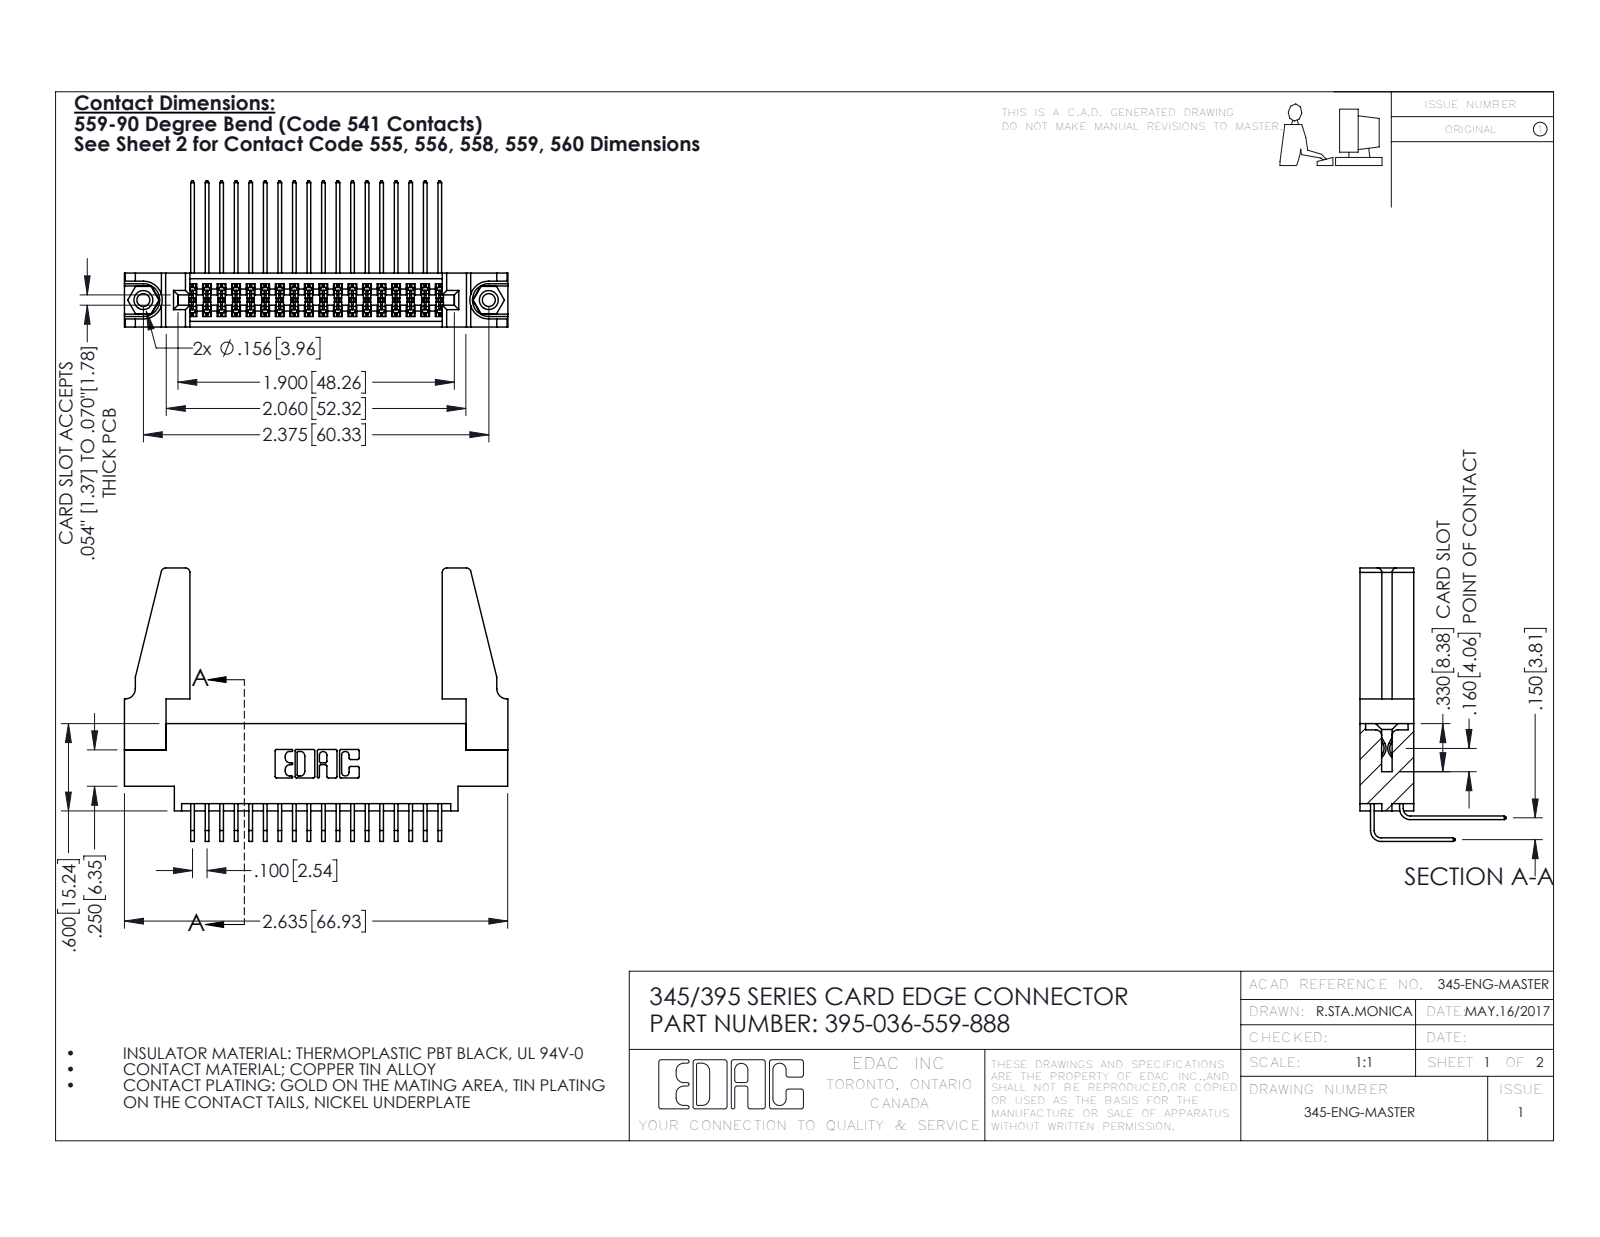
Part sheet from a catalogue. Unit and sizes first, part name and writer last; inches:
Units: inches
Overall size (bounding box): 2.636 × 1.879 × 1.005
Round holes (diameter × count): ⌀0.089 ×2, ⌀0.125 ×2, ⌀0.156 ×2, ⌀0.064 ×1
Round bosses / shafts (diameter × count): ⌀0.155 ×2
Partial cylindrical surfaces — rounded edges, fillets, slot ends (radius × count): R0.006 ×54, R0.01 ×22, R0.03 ×8, R0.007 ×6, R0.031 ×6, R0.026 ×3, R0.014 ×2, R0.019 ×2
Main face-to-face distances: 0.37, 0.072, 0.298, 0.2, 0.098, 0.272, 0.025, 0.15, 0.225, 0.175
Hole centre spacings: 0.27, 2.141, 2.375
Volume: 0.588 in³ · Surface area: 20.46 in²
Bodies: 41 solids, 2126 faces (1416 planar, 694 cylindrical, 16 other)
Part name (STEP PRODUCT): 345-292-001_559 Tail - 2; 345-292-001_558 559 Tail - 1; 345 Part_0.170 Offset - 0.156 Dia-TH; 345-250-001_345-250-001-102 (+2 more)
STEP written by: SolidWorks 2016 (CONFIG_CONTROL_DESIGN)
